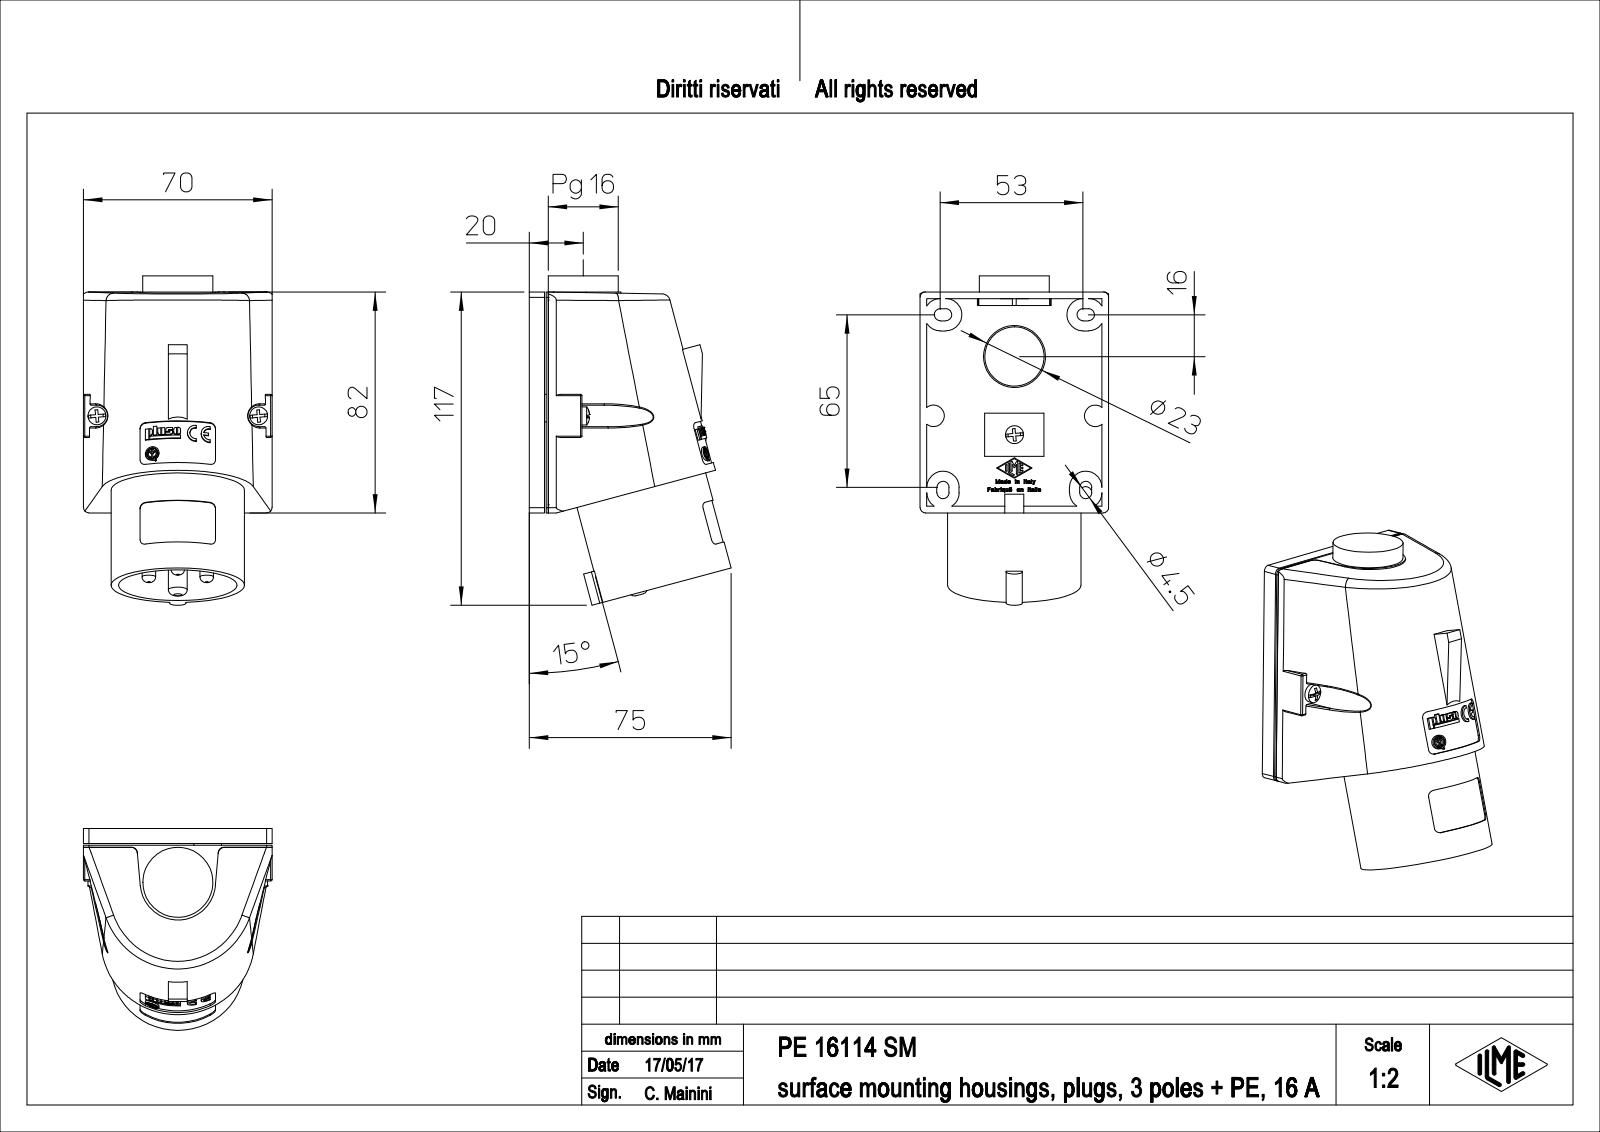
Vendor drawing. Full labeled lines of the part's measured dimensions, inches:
Part name (STEP PRODUCT): PE_16114_SM
STEP written by: PTC Creo Elements/Direct Modeling 19.0E 27-Jun-2016 (C) Parametric Technology GmbH (AUTOMOTIVE_DESIGN)
Units: inches
Bodies: 1 solid, 2014 faces (1701 planar, 233 cylindrical, 80 other)
Overall size (bounding box): 4.813 × 2.949 × 2.756
Volume: 15.27 in³ · Surface area: 97.73 in²
Round holes (diameter × count): ⌀0.236 ×4, ⌀0.126 ×2, ⌀0.165 ×2, ⌀0.169 ×2, ⌀0.177 ×2, ⌀0.118 ×1, ⌀0.839 ×1, ⌀0.906 ×1, ⌀1.732 ×1
Round bosses / shafts (diameter × count): ⌀0.197 ×6, ⌀0.264 ×5, ⌀1.024 ×2, ⌀1.949 ×1, ⌀1.654 ×1, ⌀0.403 ×1, ⌀0.276 ×1
Partial cylindrical surfaces — rounded edges, fillets, slot ends (radius × count): R0.02 ×17, R0.01 ×15, R0.079 ×15, R0.236 ×12, R0.034 ×9, R0.089 ×8, R0.157 ×8, R0.039 ×6
Main face-to-face distances: 0.098, 0.237, 0.139, 0.138, 0.108, 0.031, 0.206, 0.025, 0.083, 0.056
Hole centre spacings: 0.423, 0.598, 0.599, 0.846, 1.213, 1.465, 0.424, 1.142
